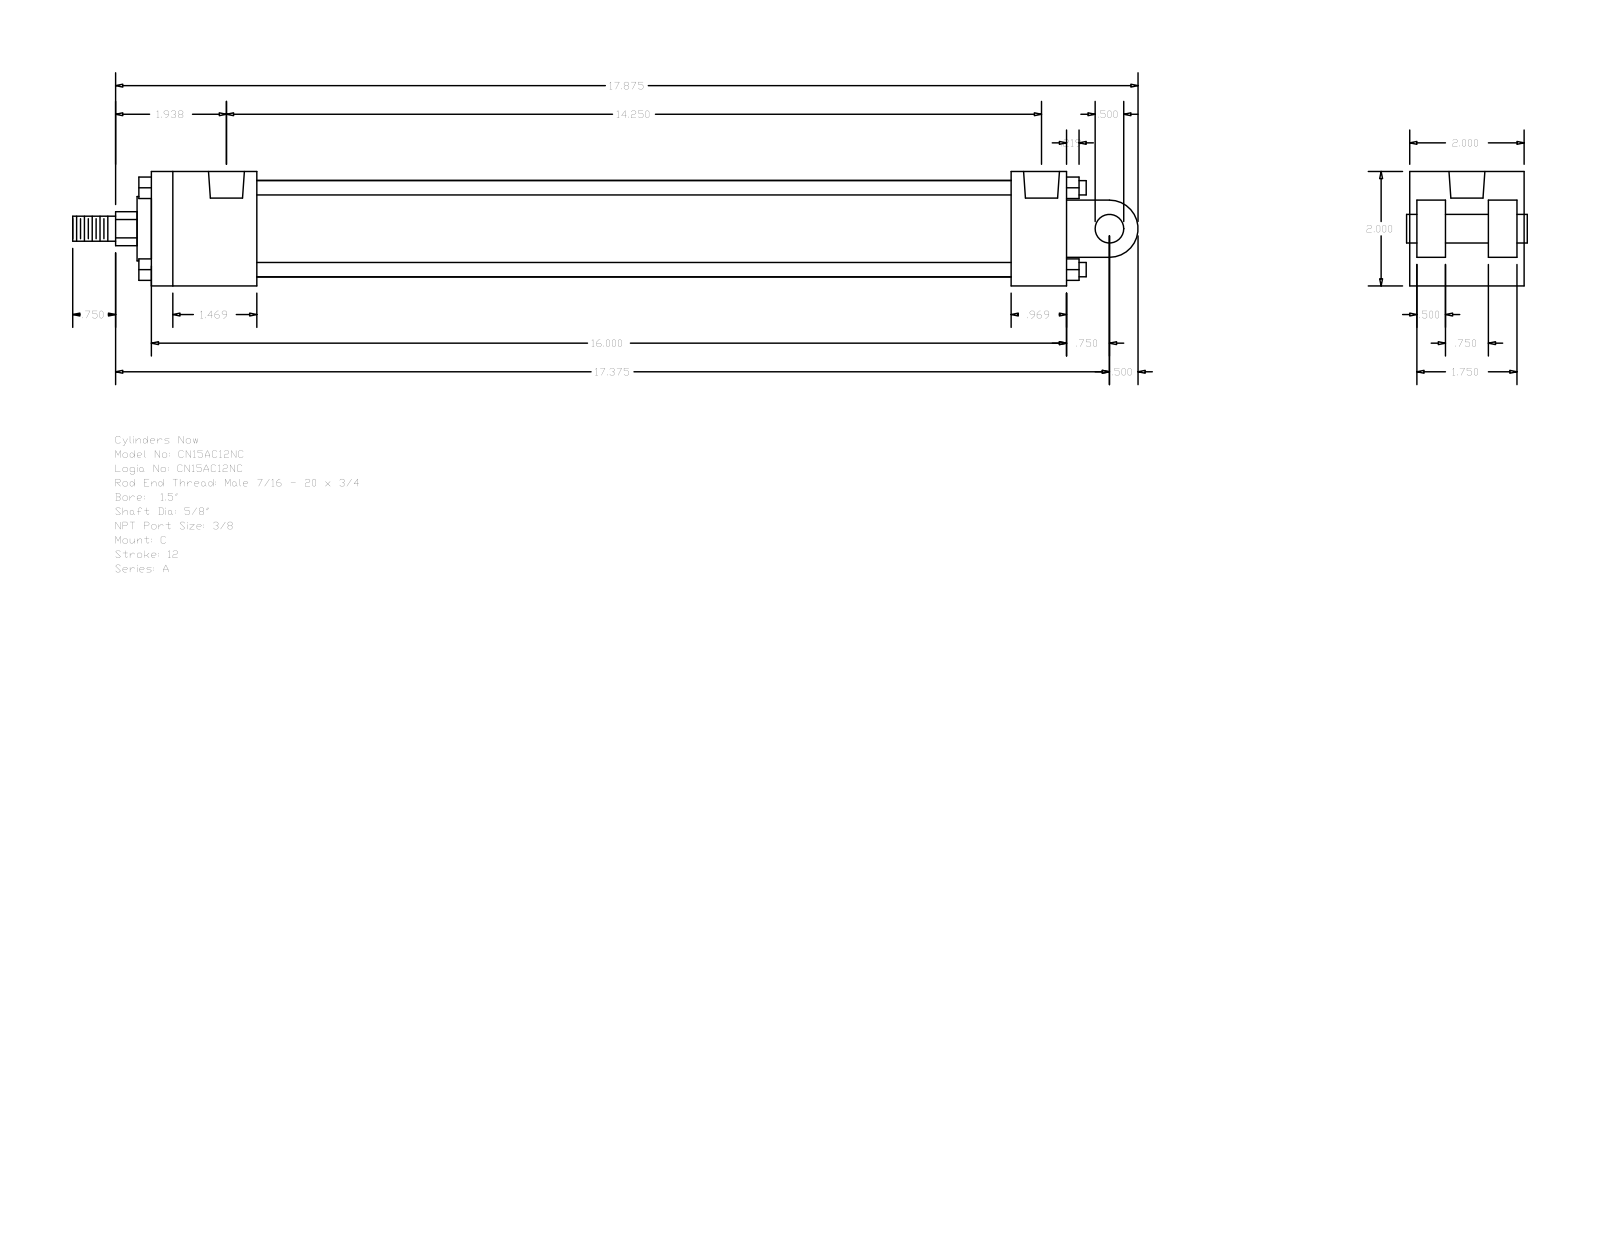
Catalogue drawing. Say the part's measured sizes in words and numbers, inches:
The part is named "A_C__0150_0.625". Its 3-D file was written by "GSSL Pune (CONFIG_CONTROL_DESIGN)". It is 0 solids with 135 faces: 102 planar, 33 cylindrical and 0 other. Overall it measures 18.625 by 2 by 2 inches. Round holes: 4 of diameter 0.219, 2 of diameter 0.627. Round bosses or shafts: 4 of diameter 0.25, 1 of diameter 1.69, 1 of diameter 1.125, 1 of diameter 0.625, 1 of diameter 0.5, 1 of diameter 0.437. Partial cylindrical surfaces (rounded edges, fillets, slot ends): 1 of radius 0.297, 1 of radius 0.5. The main face-to-face distances are 2, 0.5, 16, 1.375, 0.125, 0.625, 1.875, 1.25, 15.031, 0.969. The hole center spacings are 0.156, 13.937, 14.094, 14.25.
